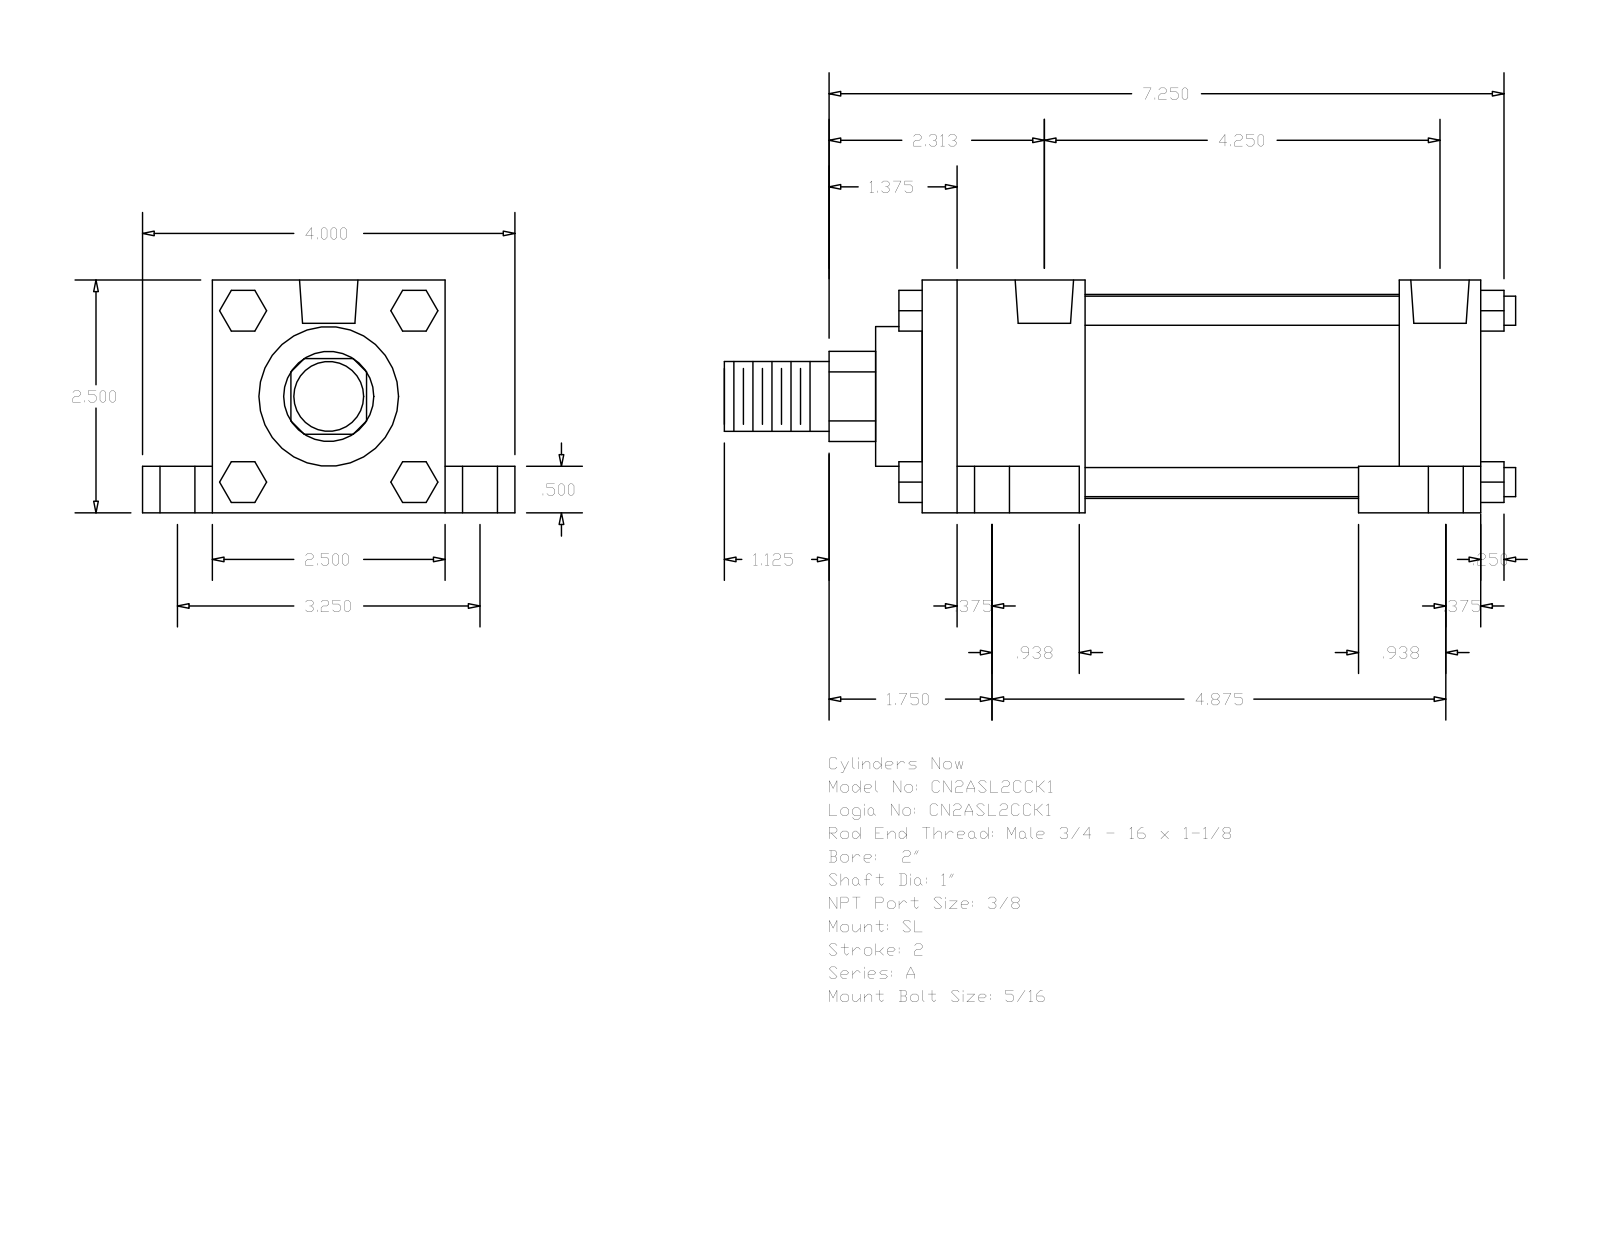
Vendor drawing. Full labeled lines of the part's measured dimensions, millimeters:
Part name (STEP PRODUCT): A_SL__0200_1
STEP written by: GSSL Pune (CONFIG_CONTROL_DESIGN)
Units: millimetres
Bodies: 0 solids, 148 faces (112 planar, 36 cylindrical, 0 other)
Overall size (bounding box): 215.9 × 101.6 × 63.5
Round holes (diameter × count): ⌀5.56 ×4, ⌀9.53 ×4, ⌀15.88 ×4, ⌀15.93 ×2
Round bosses / shafts (diameter × count): ⌀7.94 ×4, ⌀55.63 ×1, ⌀38.1 ×1, ⌀25.4 ×1, ⌀19.05 ×1
Partial cylindrical surfaces — rounded edges, fillets, slot ends (radius × count): R12.29 ×1
Main face-to-face distances: 63.5, 152.4, 12.7, 50.8, 19.05, 82.55, 44.45, 107.95, 130.17, 85.72
Hole centre spacings: 41.3, 41.64, 43.67, 44.22, 82.54, 102.38, 115.57, 117.06
